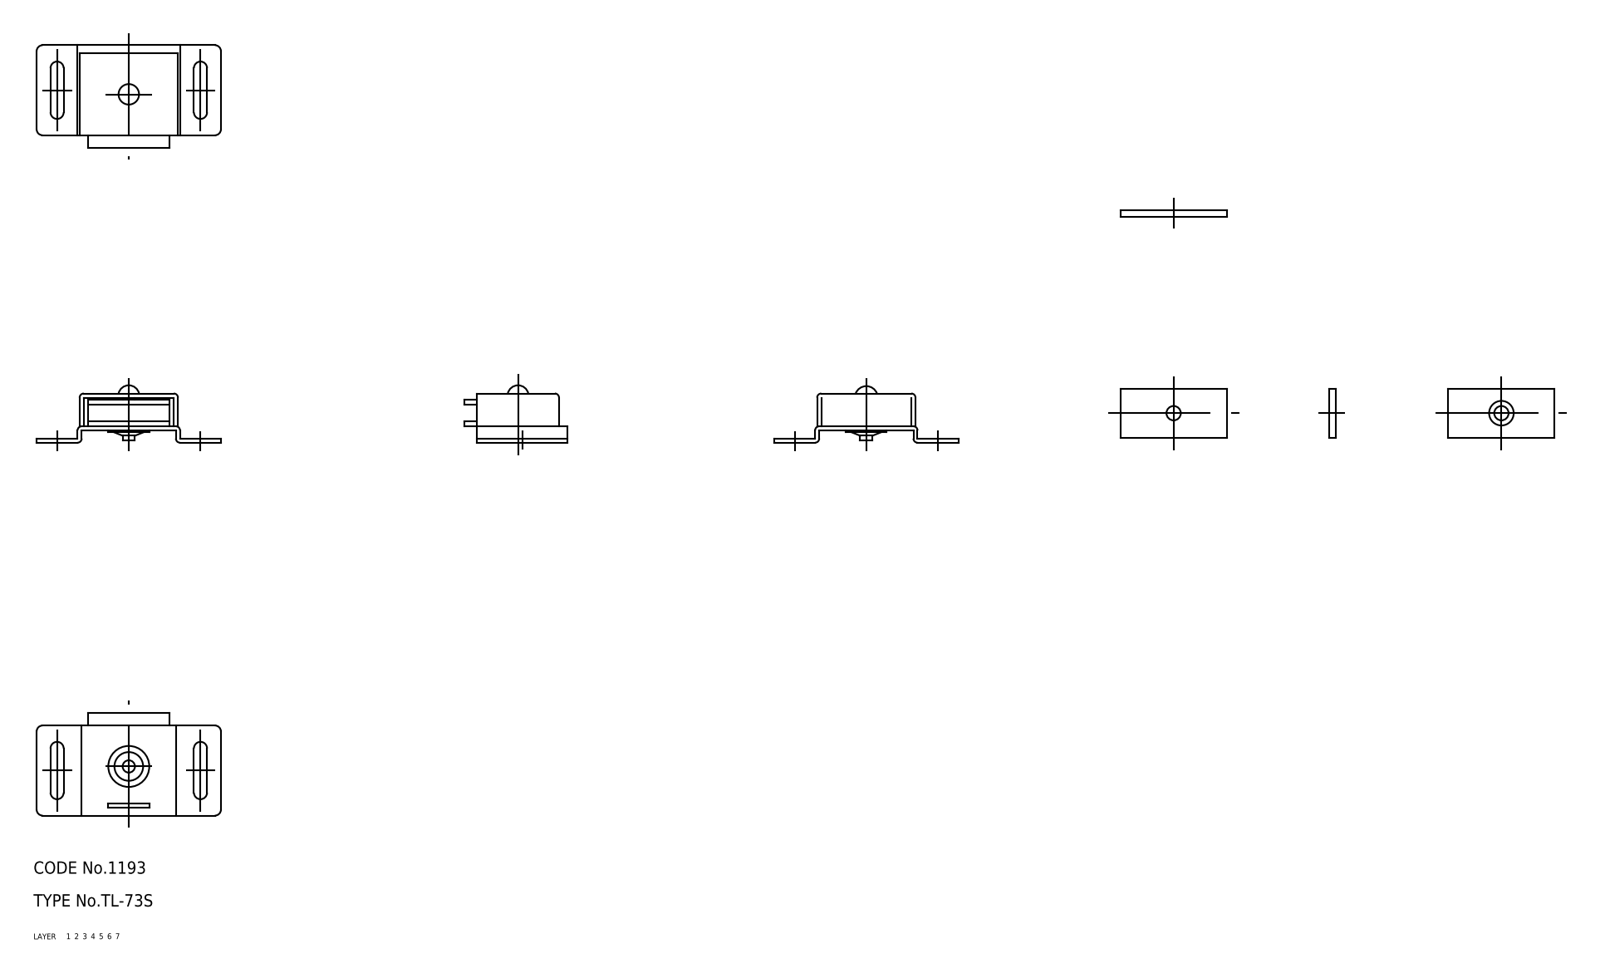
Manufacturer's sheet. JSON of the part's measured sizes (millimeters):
{"part_name": "67113964; 67113977; 67113990; 67114003 (+4 more)", "step_written_by": "CADfix (AUTOMOTIVE_DESIGN)", "units": "millimeters", "bodies": {"solids": 8, "faces": 113, "planar": 0, "cylindrical": 0, "other": 113}, "overall_size": [48.6, 45, 14], "volume_mm3": 4530, "surface_area_mm2": 7764}
